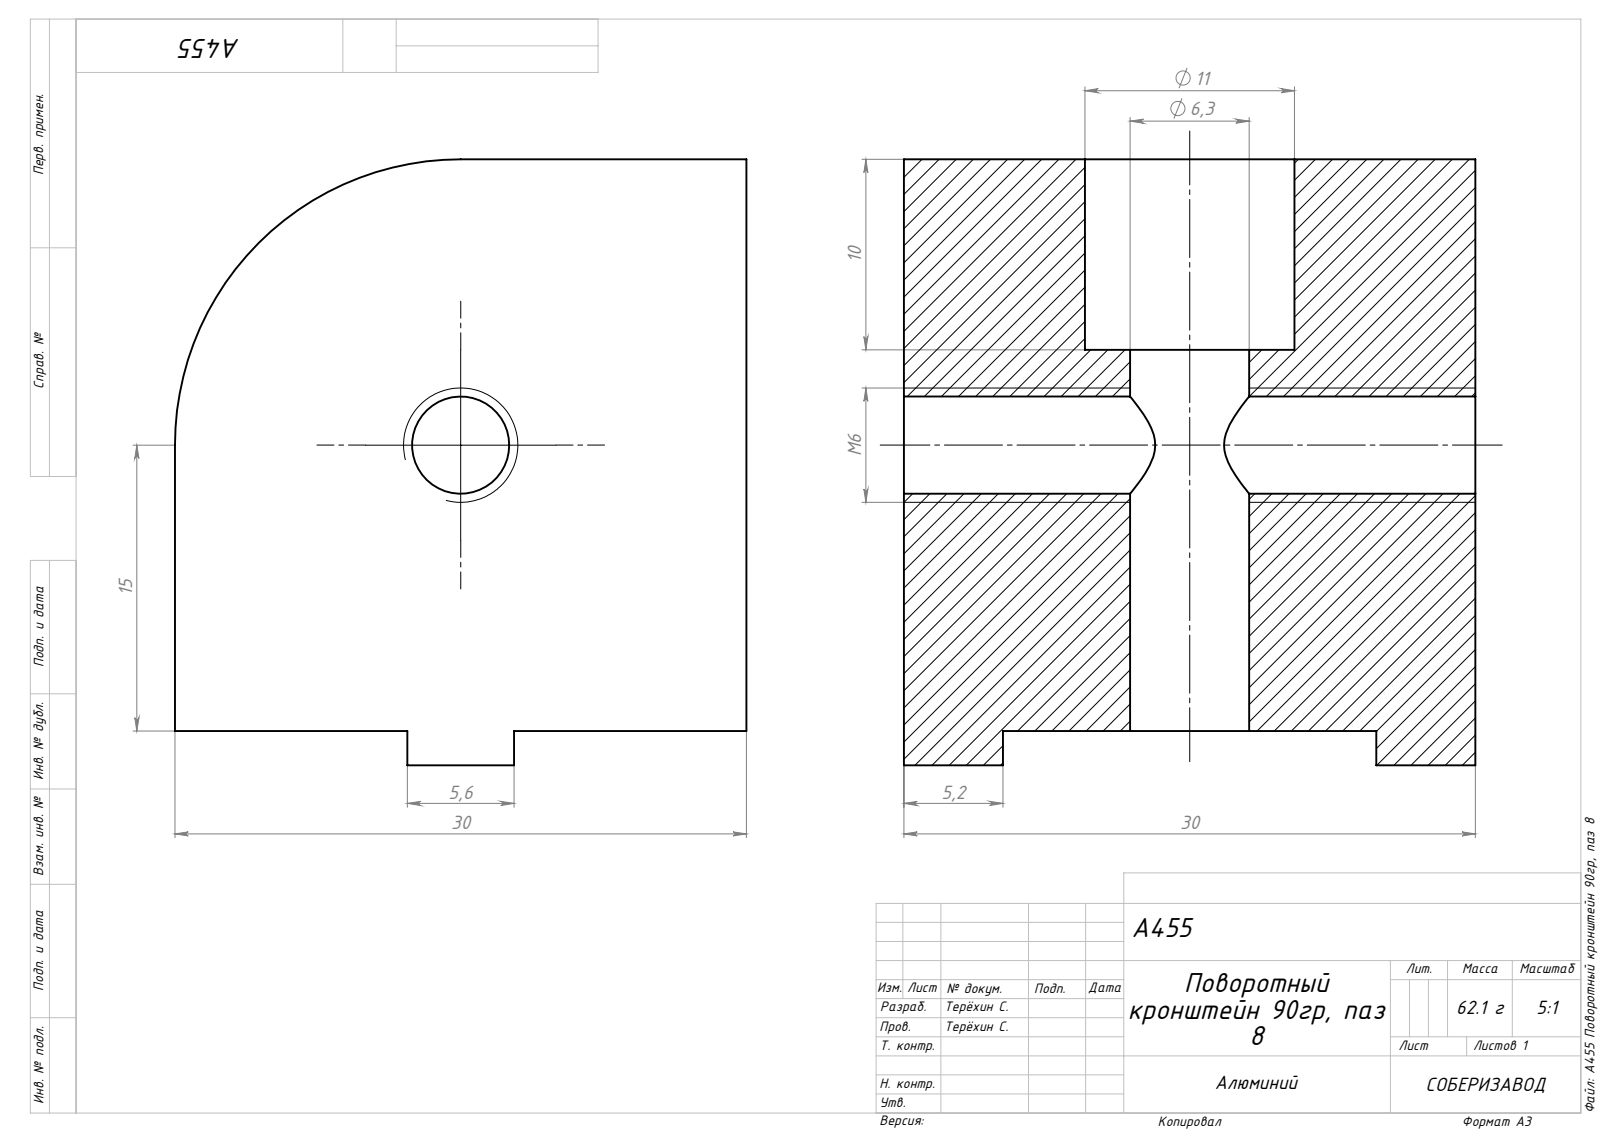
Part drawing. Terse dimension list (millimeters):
name: Сборка1; A455 Поворотный кронштейн 90гр, паз 8
written by: SolidWorks 2021 (AUTOMOTIVE_DESIGN)
unit: mm
bodies: 1 solid, 24 faces (15 planar, 9 cylindrical, 0 other)
size: 31.8 × 30 × 30
volume: 23 608 mm³; area: 6 169 mm²
holes: 1× ⌀5.1, 1× ⌀6.25, 1× ⌀11
rounds: 1× R15
face distances: 30, 20, 10, 1.8, 21.8, 31.8, 12.2, 17.8, 5.2, 24.8
